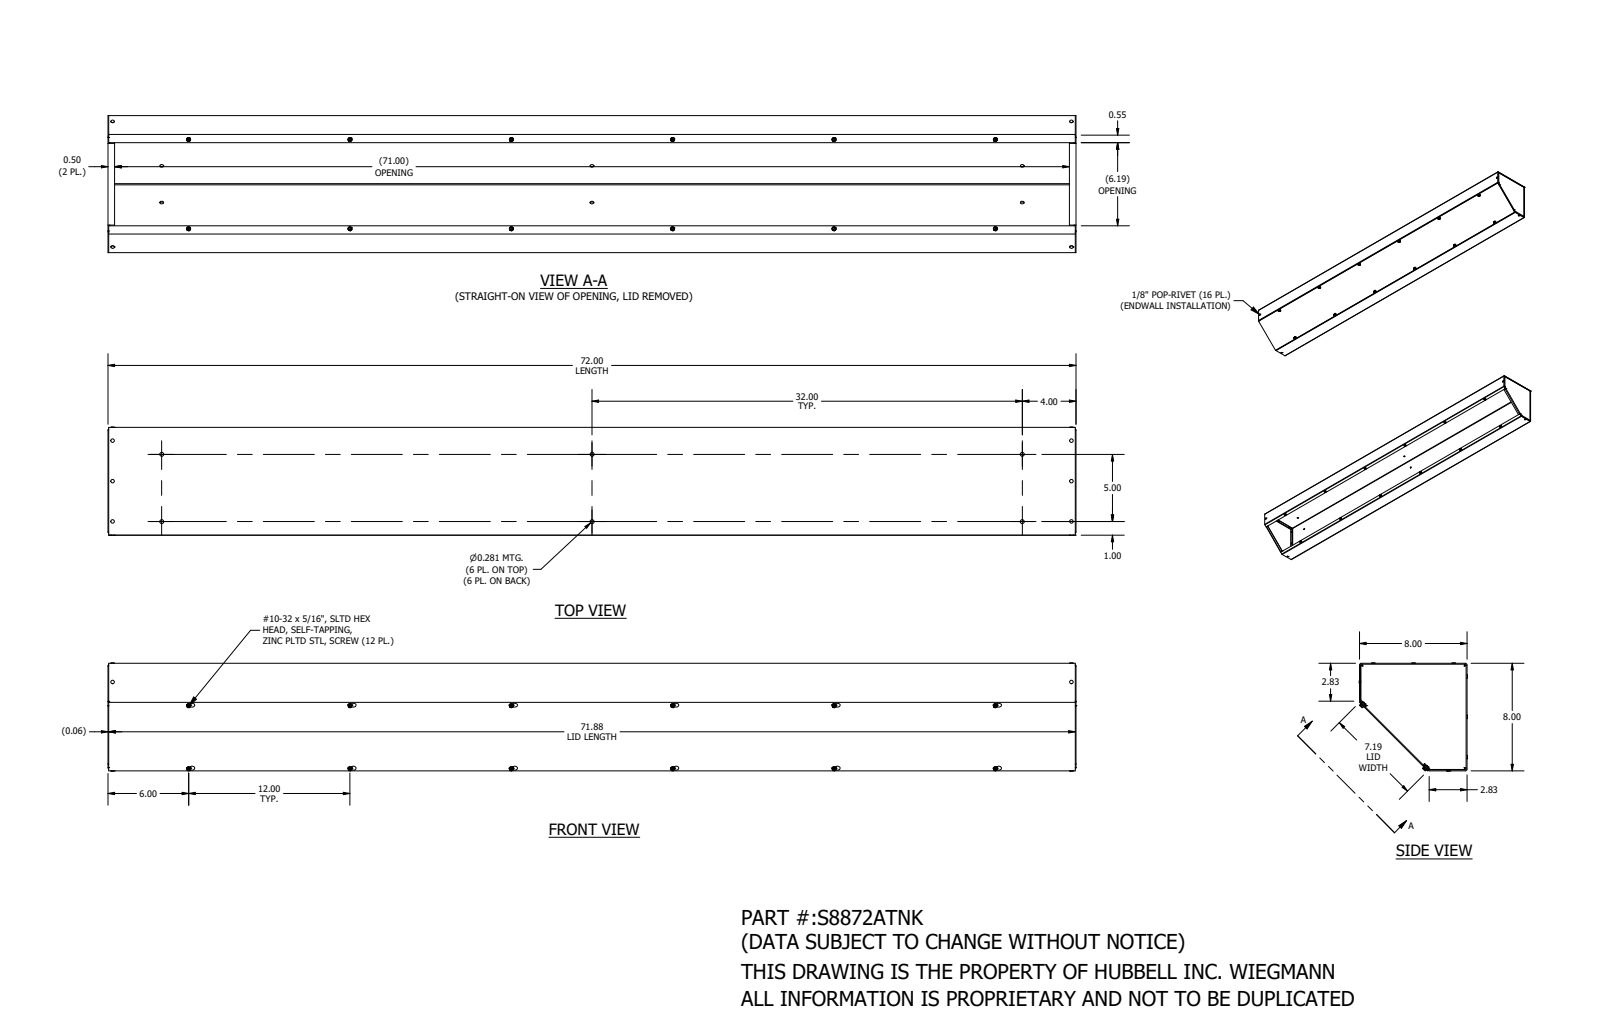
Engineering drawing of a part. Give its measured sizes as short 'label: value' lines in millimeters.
name: S8872ATNK
written by: SolidWorks 2021 (AUTOMOTIVE_DESIGN)
unit: mm
bodies: 32 solids, 2252 faces (484 planar, 576 cylindrical, 1192 other)
size: 1828.8 × 205.2 × 205.2
volume: 2 719 000 mm³; area: 2 917 000 mm²
holes: 16× ⌀3.3, 12× ⌀4.3, 12× ⌀7.1, 12× ⌀10.3
bosses: 16× ⌀6.7, 12× ⌀8, 12× ⌀4.6, 8× ⌀3.2, 8× ⌀3.2
rounds: 32× R1.6, 15× R3.5, 12× R2.8, 9× R1.6, 6× R1.6
face distances: 1.9, 201.3, 199.4, 203.2, 1.7, 1826.9, 3.6, 1825, 1828.8, 3.8
hole spacings: 304.8, 609.6, 6.4, 914.4, 298.5, 311.2, 348.2, 348.3
